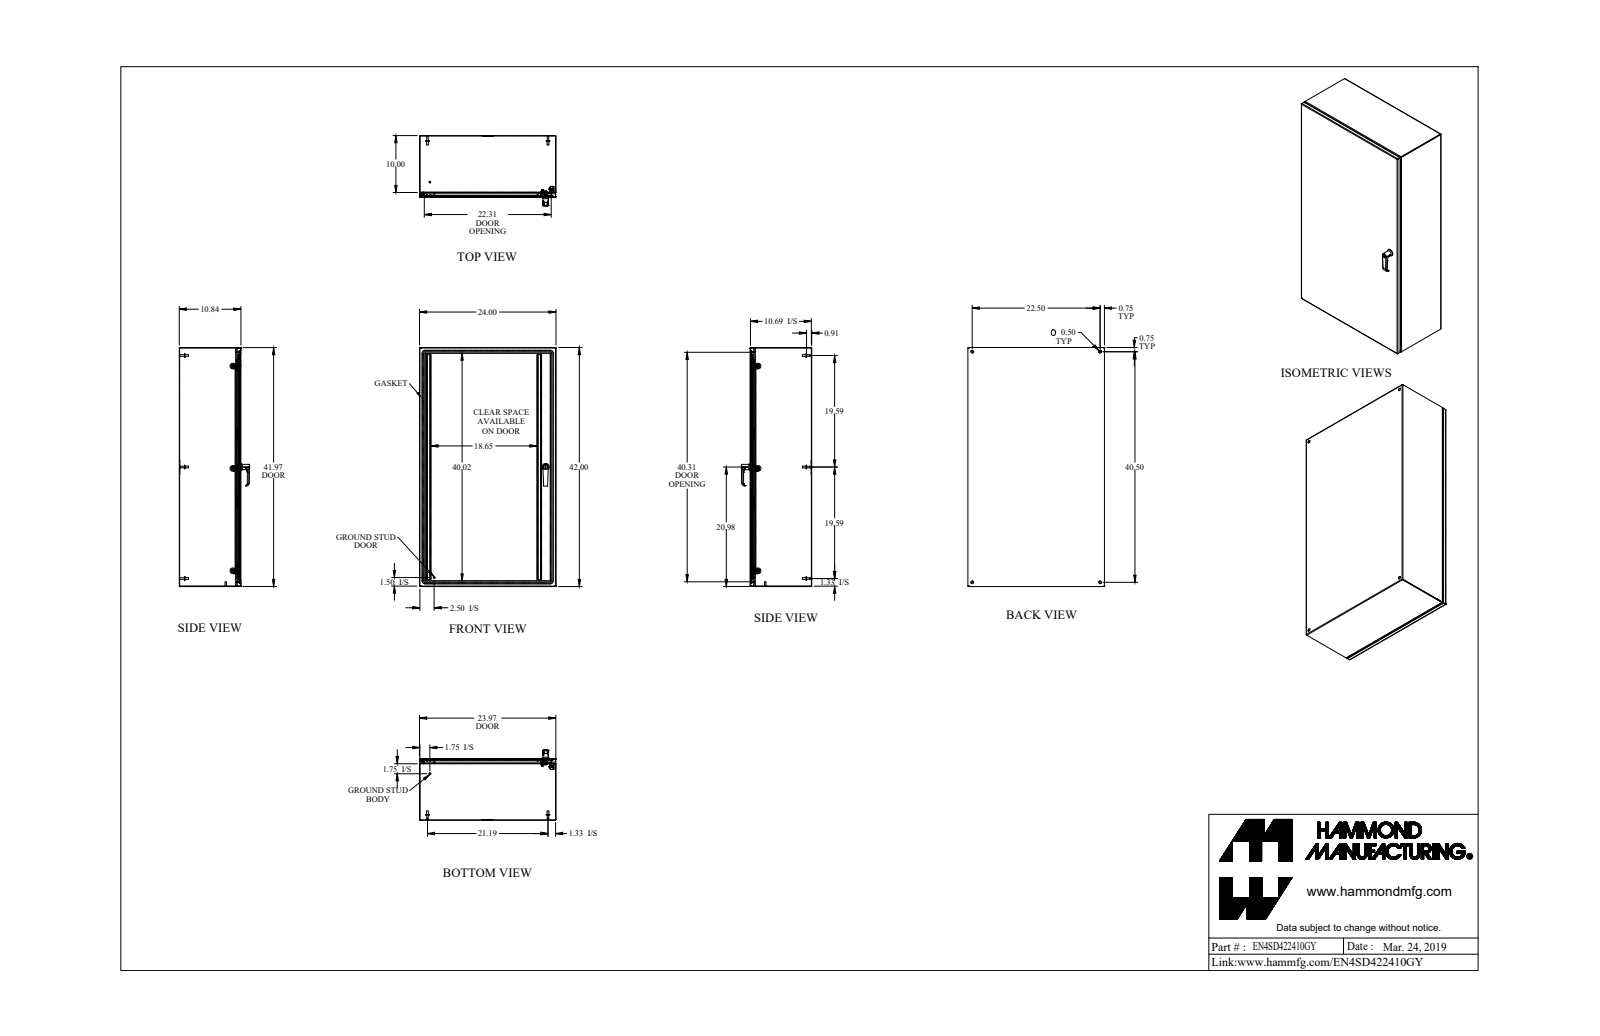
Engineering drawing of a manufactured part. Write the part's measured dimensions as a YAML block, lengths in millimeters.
part_name: "EN4SD422410GY"
step_written_by: "SolidWorks 2019 (AUTOMOTIVE_DESIGN)"
units: millimeters
bodies: {solids: 53, faces: 1457, planar: 632, cylindrical: 538, other: 287}
overall_size: [1066.8, 609.6, 314.1]
volume: 4683000
surface_area: 5112000
round_holes:
  - {diameter: 4.5, count: 6}
  - {diameter: 12.7, count: 4}
  - {diameter: 5, count: 3}
  - {diameter: 6.4, count: 3}
  - {diameter: 6.7, count: 3}
  - {diameter: 10.5, count: 3}
  - {diameter: 6.5, count: 2}
  - {diameter: 8, count: 2}
  - {diameter: 10, count: 2}
  - {diameter: 4.4, count: 1}
  - {diameter: 6.1, count: 1}
  - {diameter: 6.1, count: 1}
round_bosses_or_shafts:
  - {diameter: 6.4, count: 7}
  - {diameter: 9.5, count: 6}
  - {diameter: 8, count: 6}
  - {diameter: 6.9, count: 6}
  - {diameter: 4, count: 6}
  - {diameter: 15.9, count: 4}
  - {diameter: 25.4, count: 3}
  - {diameter: 16, count: 2}
partial_cylinders:
  - {radius: 0.9, count: 20}
  - {radius: 2.7, count: 20}
  - {radius: 0.8, count: 15}
  - {radius: 1.1, count: 12}
  - {radius: 2.1, count: 12}
  - {radius: 0.2, count: 8}
  - {radius: 1, count: 8}
  - {radius: 1.6, count: 8}
face_to_face_distances: [1.8, 273.4, 271.6, 275.3, 607.8, 1065, 605.9, 609.6, 1063.1, 1066.8]
hole_center_spacings: [20, 456.7, 457.2, 534.9, 571.5, 913.6, 1028.7, 1176.8]
